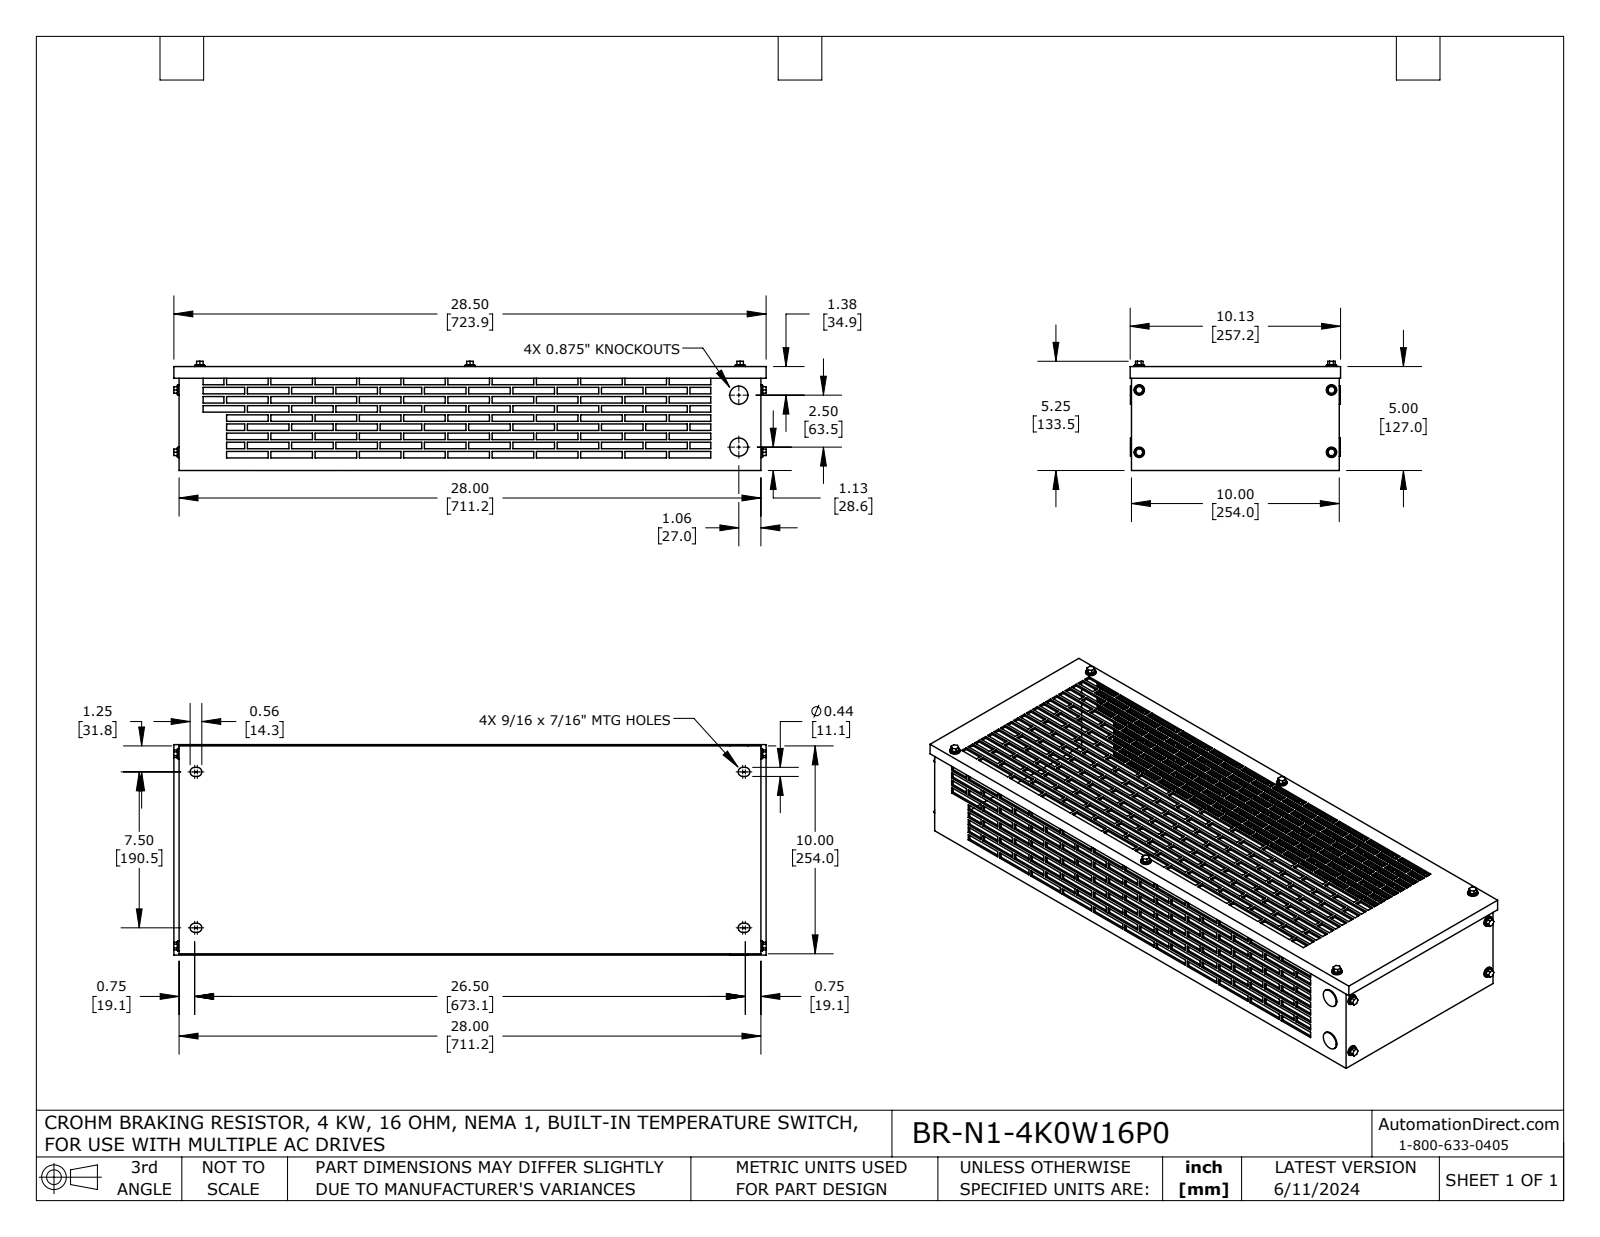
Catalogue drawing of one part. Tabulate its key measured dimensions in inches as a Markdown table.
| quantity | value |
| --- | --- |
| part name | BR-N1-4K0W16P0 |
| STEP written by | SolidWorks 2021 (AUTOMOTIVE_DESIGN) |
| units | inches |
| bodies | 33 solids, 2040 faces (1932 planar, 108 cylindrical, 0 other) |
| overall size | 28.509 × 10.125 × 5.254 |
| volume | 68.03 in³ |
| surface area | 1 567 in² |
| round holes (diameter × count) | 0.25 × 10, 0.75 × 2 |
| round bosses / shafts (diameter × count) | 0.5 × 10, 0.437 × 10, 0.875 × 2 |
| partial cylindrical surfaces (radius × count) | 0.219 × 8 |
| main face-to-face distances | 0.1, 4.9, 5, 4.8, 9.9, 27.9, 10, 9.8, 0.88, 0.063 |
| hole center spacings | 9.25, 13, 15.955, 3, 9.724, 26, 27.596, 2.5 |
